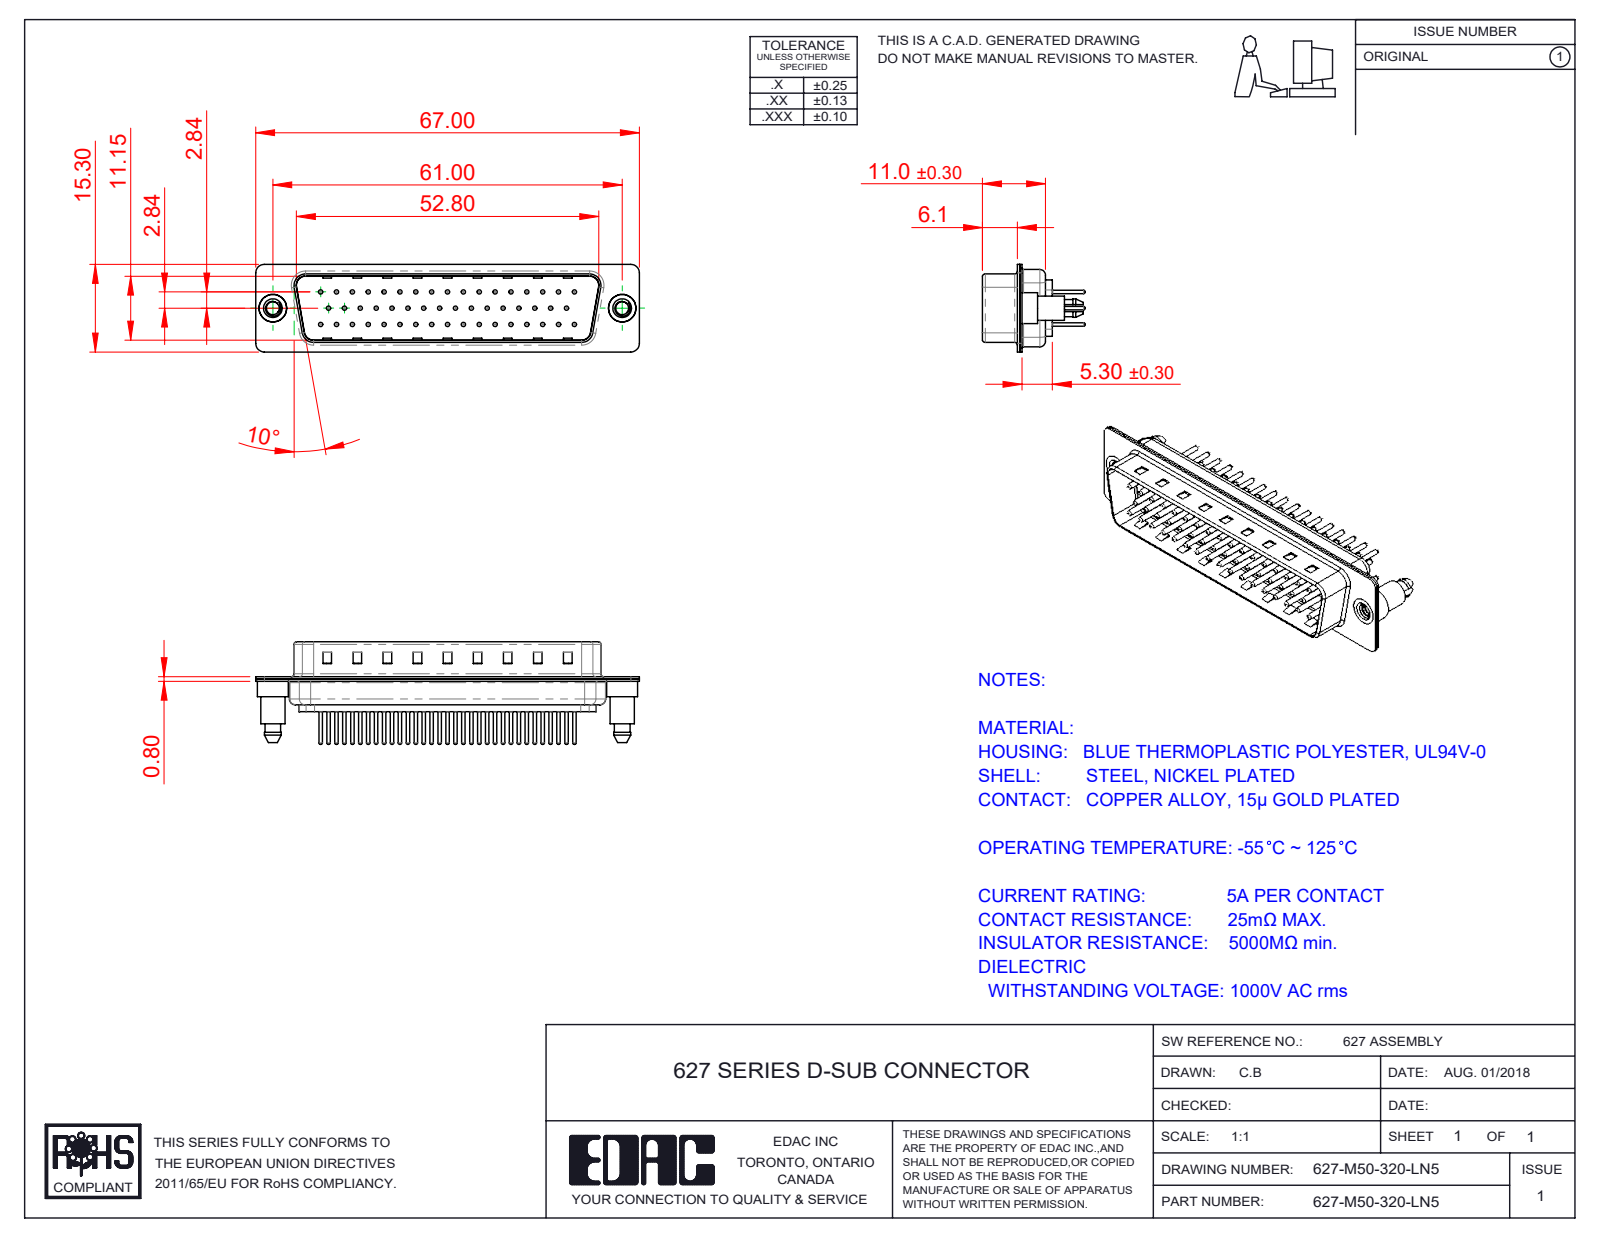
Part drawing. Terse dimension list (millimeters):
name: 627M Shell Front_50 Contacts; 627M 4-40 Threaded Boardlock; 627M Shell Rear_50 Contacts; 627M Contact Row 2_20 (+4 more)
written by: SolidWorks 2020 (CONFIG_CONTROL_DESIGN)
unit: mm
bodies: 55 solids, 2312 faces (569 planar, 873 cylindrical, 870 other)
size: 67 × 17.9 × 15.3
volume: 4 659 mm³; area: 11 032 mm²
holes: 50× ⌀0.75, 50× ⌀1.6, 50× ⌀2, 2× ⌀2.26, 2× ⌀4, 2× ⌀4.8
bosses: 50× ⌀1.5, 50× ⌀0.6, 2× ⌀5.4, 2× ⌀4.9, 2× ⌀4.25
rounds: 18× R1.5, 12× R2, 10× R1.6, 8× R0.5, 4× R0.25, 4× R0.6, 4× R0.65, 4× R0.9
face distances: 0.4, 11.55, 5.7, 6.1, 0.78, 0.77, 12.33, 5.3, 12.32, 13.1
hole spacings: 3.16, 2.77, 5.54, 8.31, 11.08, 13.85, 16.62, 5.03
